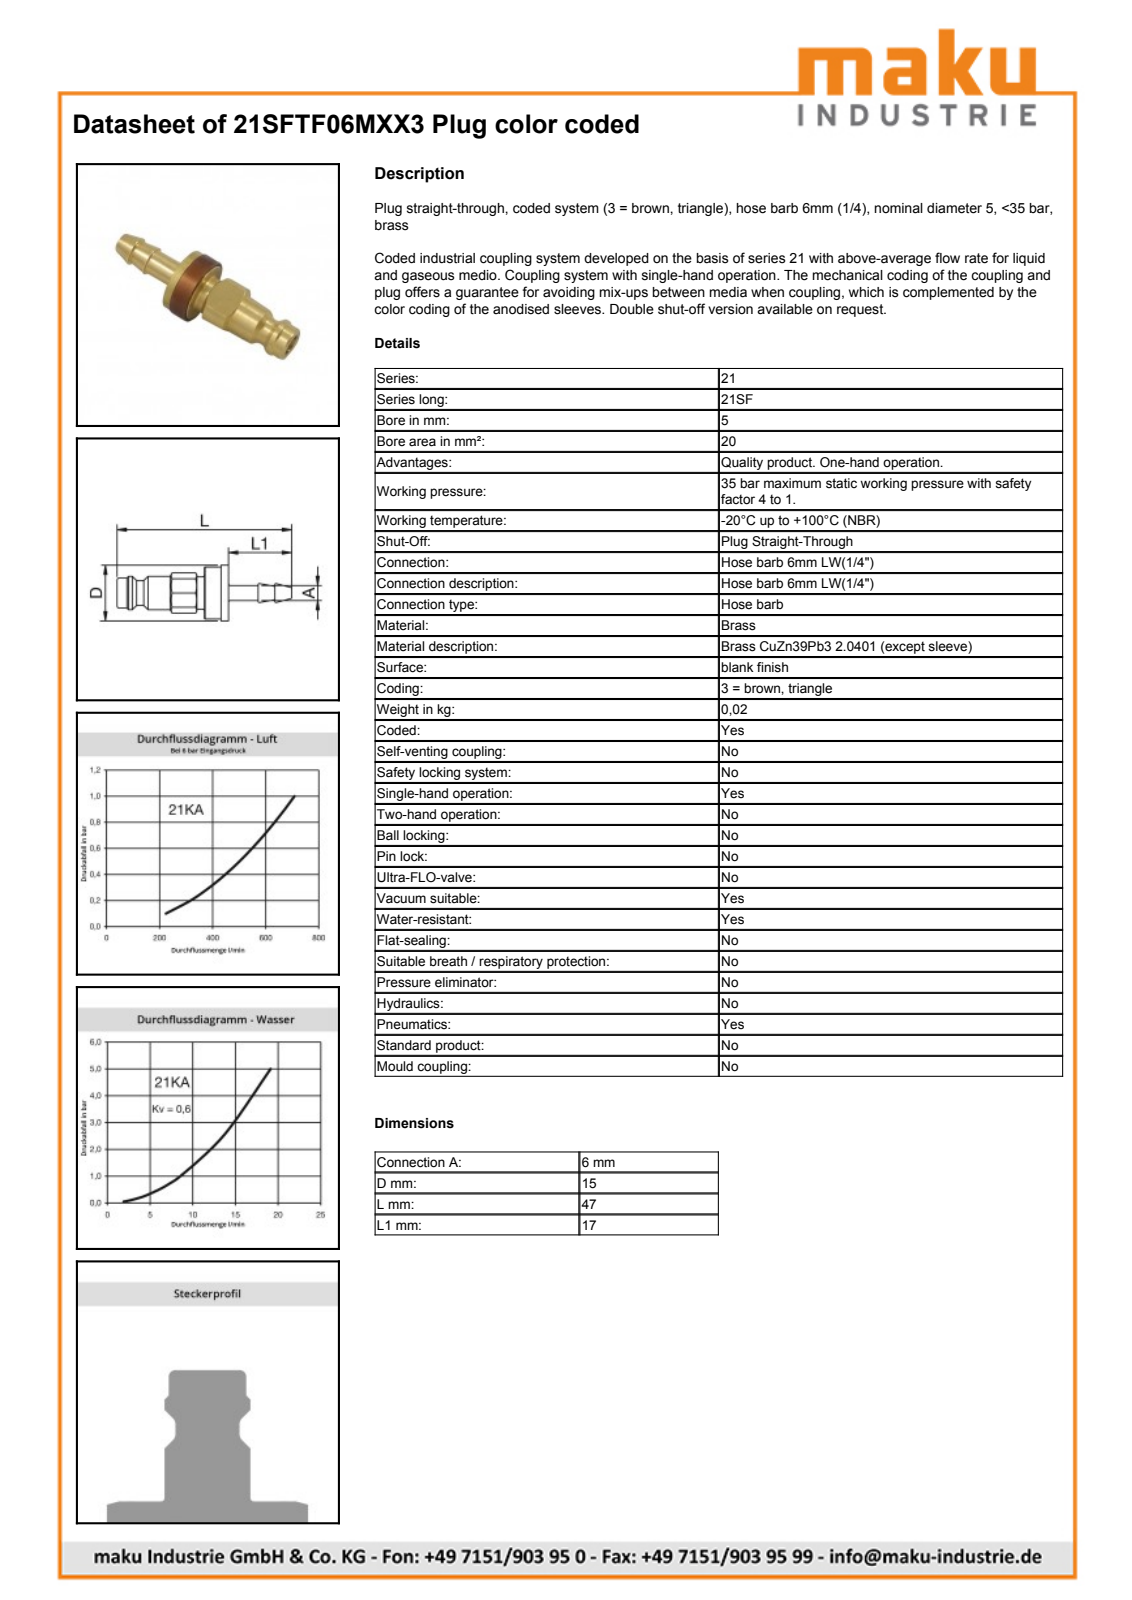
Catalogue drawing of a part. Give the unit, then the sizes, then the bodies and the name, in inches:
Units: inches
Overall size (bounding box): 1.85 × 0.61 × 0.61
Round holes (diameter × count): ⌀0.157 ×1, ⌀0.195 ×1, ⌀0.545 ×1, ⌀0.553 ×1
Round bosses / shafts (diameter × count): ⌀0.61 ×1, ⌀0.591 ×1, ⌀0.551 ×1, ⌀0.354 ×1, ⌀0.343 ×1, ⌀0.319 ×1, ⌀0.262 ×1, ⌀0.238 ×1
Partial cylindrical surfaces — rounded edges, fillets, slot ends (radius × count): R0.232 ×1
Main face-to-face distances: 0.256, 0.177, 0.079, 0.165, 0.244, 0.925, 0.937, 1.102, 1.181, 0.571
Volume: 0.155 in³ · Surface area: 4.331 in²
Bodies: 2 solids, 50 faces (12 planar, 16 cylindrical, 22 other)
Part name (STEP PRODUCT): D103766; D103765; D103012
STEP written by: Autodesk Inventor 2011 (AUTOMOTIVE_DESIGN)
